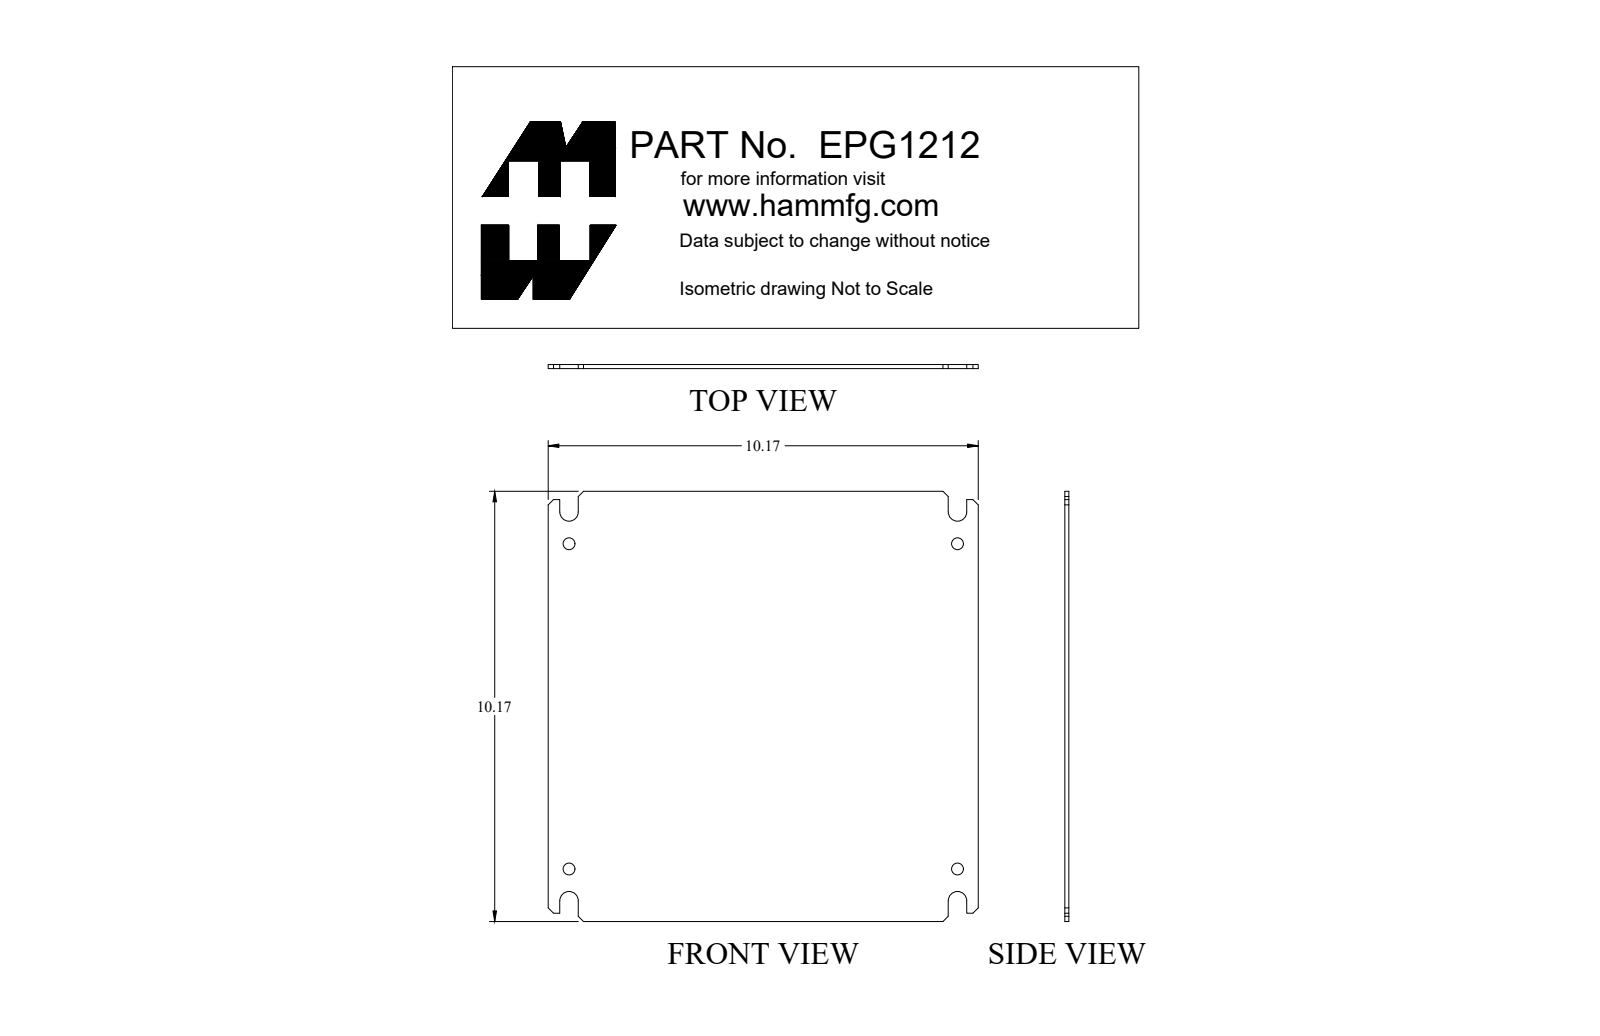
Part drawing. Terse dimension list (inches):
name: EPG1212
written by: SolidWorks 2018 (AUTOMOTIVE_DESIGN)
unit: in
bodies: 1 solid, 40 faces (26 planar, 14 cylindrical, 0 other)
size: 10.17 × 10.17 × 0.095
volume: 9.666 in³; area: 208 in²
holes: 4× ⌀0.281
rounds: 4× R0.219
face distances: 0.095, 10.17, 0.709, 9.461, 0.272, 9.898, 0.437, 9.188, 8.751, 0.362
hole spacings: 7.688, 9.188, 11.98
